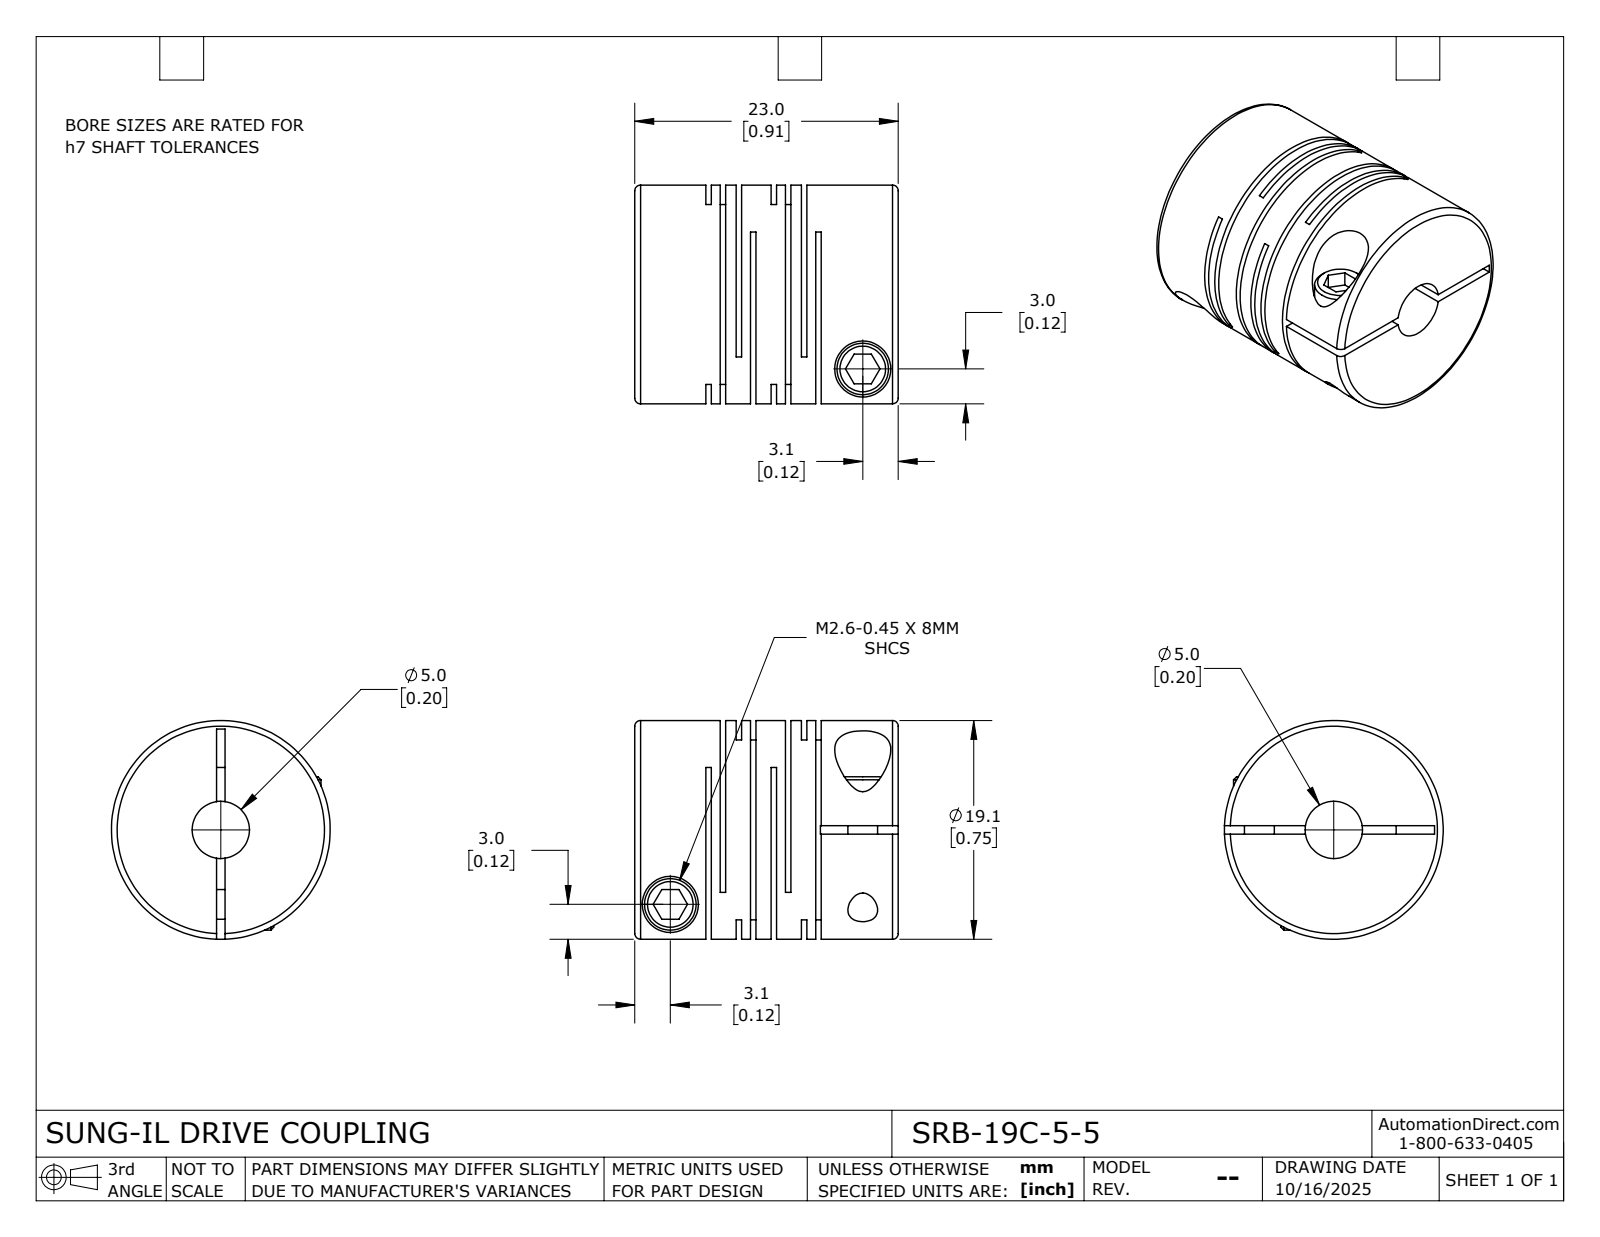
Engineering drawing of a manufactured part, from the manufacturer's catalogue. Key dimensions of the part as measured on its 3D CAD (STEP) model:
Part name (STEP PRODUCT): SRB-19C-5-5
STEP written by: SolidWorks 2024 (CONFIG_CONTROL_DESIGN)
Units: millimetres
Bodies: 1 solid, 115 faces (60 planar, 42 cylindrical, 13 other)
Overall size (bounding box): 23 × 19.1 × 19.1
Volume: 5 034 mm³ · Surface area: 6 132 mm²
Round holes (diameter × count): ⌀2.6 ×2, ⌀4.9 ×2, ⌀5 ×1
Round bosses / shafts (diameter × count): ⌀4.5 ×2, ⌀19.1 ×1
Main face-to-face distances: 2.65, 5.7, 0.48, 1.25, 2.17, 3.05, 5.22, 0.77, 4.45, 1.4
